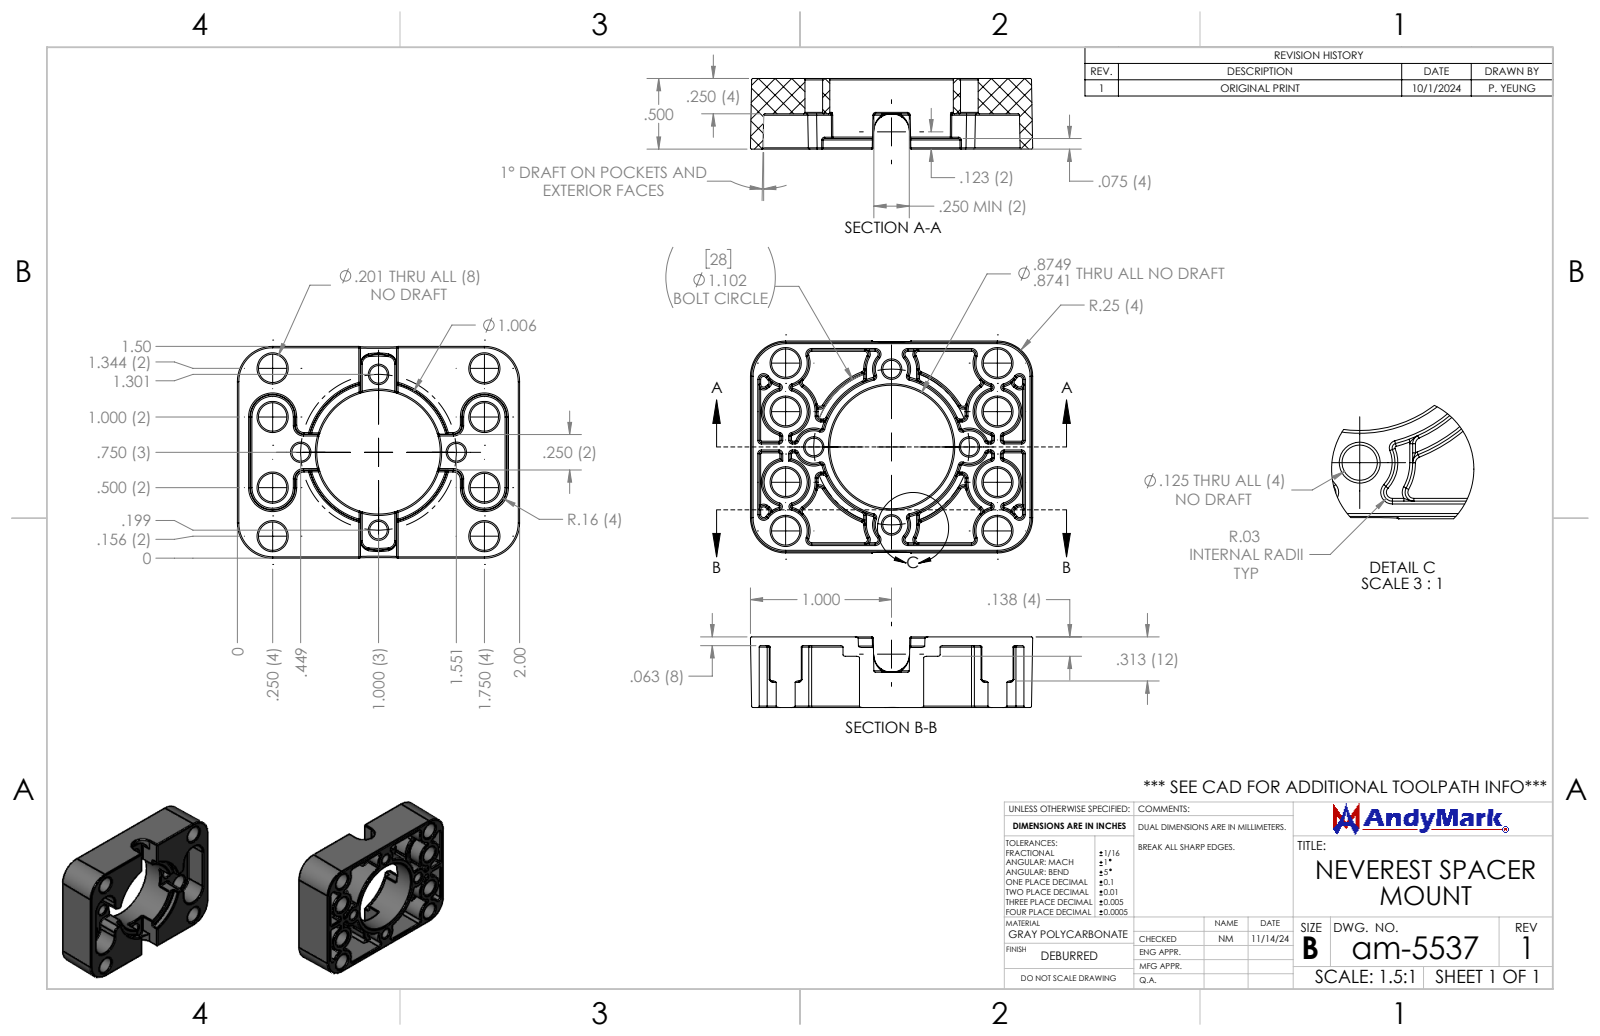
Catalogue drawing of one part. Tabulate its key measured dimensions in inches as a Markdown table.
| quantity | value |
| --- | --- |
| part name | am-5537 NeveRest Spacer Mount |
| STEP written by | SolidWorks 2024 (AUTOMOTIVE_DESIGN) |
| units | inches |
| bodies | 1 solid, 1110 faces (109 planar, 187 cylindrical, 814 other) |
| overall size | 2 × 1.5 × 0.5 |
| volume | 0.523 in³ |
| surface area | 16.06 in² |
| round holes (diameter × count) | 0.201 × 8, 0.125 × 4, 0.875 × 1 |
| partial cylindrical surfaces (radius × count) | 0.01 × 74, 0.031 × 8, 0.062 × 8, 0.127 × 1 |
| main face-to-face distances | 0.25, 1.436, 0.5, 0.063, 0.187, 0.437, 1.936, 1.847, 0.089, 1.066 |
| hole center spacings | 0.319, 0.344, 0.551, 0.626, 0.751, 0.78, 0.791, 0.808 |
